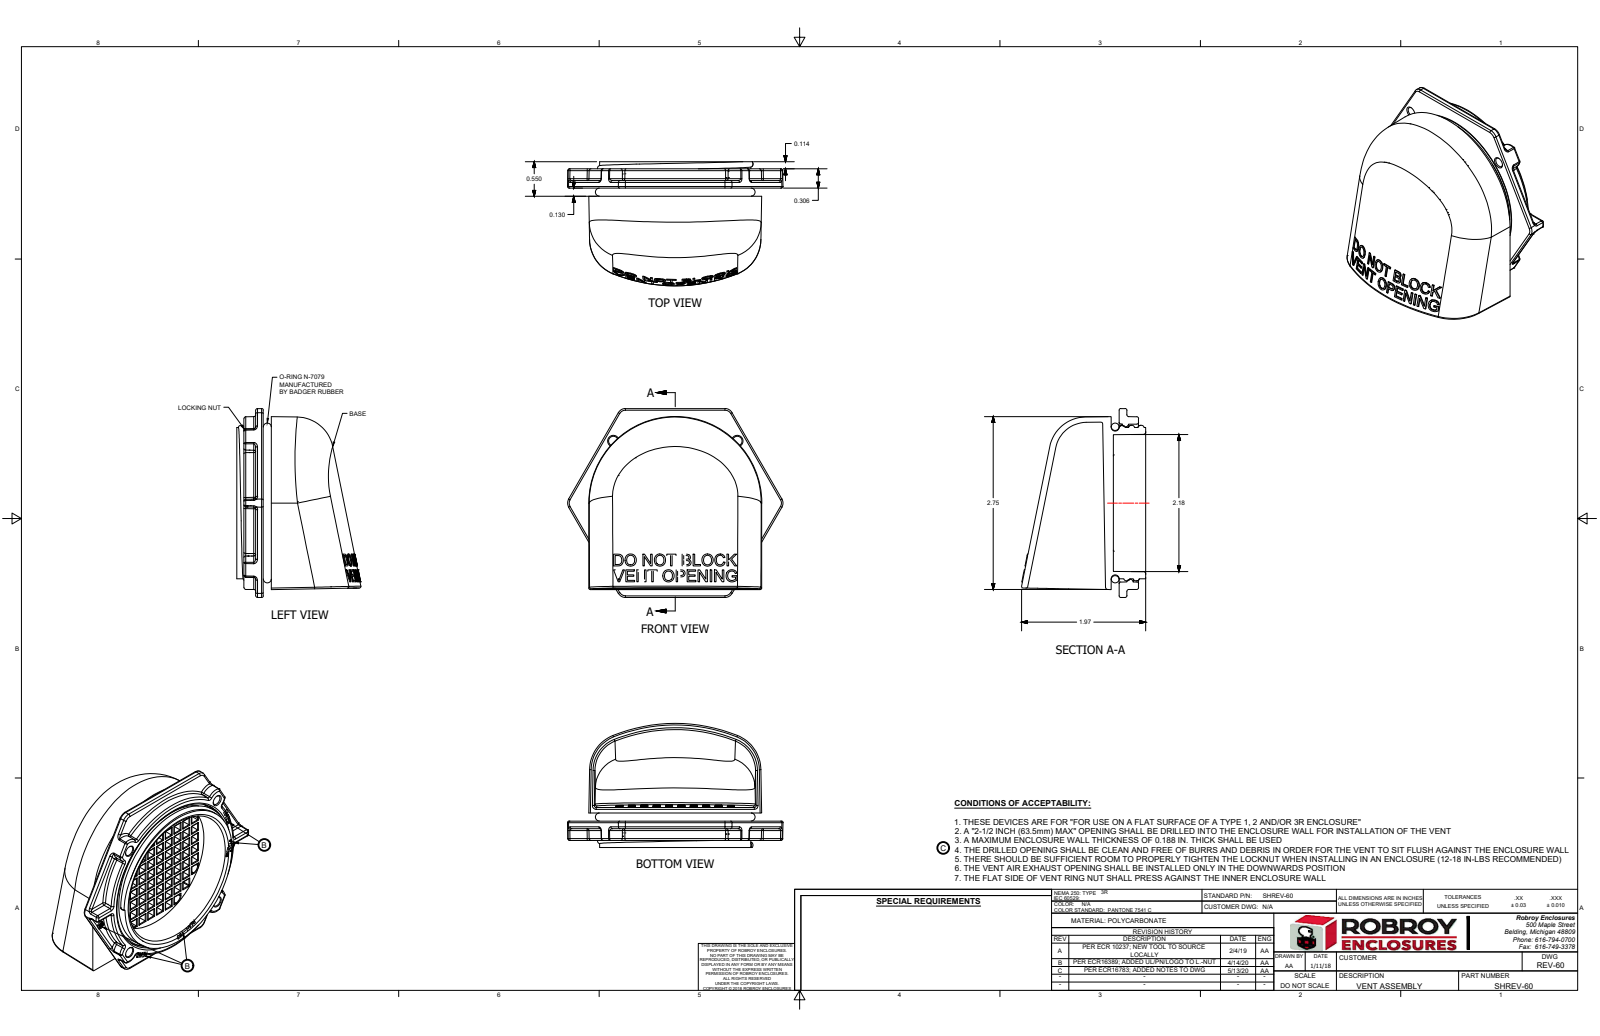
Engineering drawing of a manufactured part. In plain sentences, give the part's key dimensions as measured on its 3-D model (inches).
The part is named "REAHV-60". Its 3-D file was written by "SolidWorks 2019 (AUTOMOTIVE_DESIGN)". It is 3 solids with 1328 faces: 525 planar, 431 cylindrical and 372 other. Overall it measures 3.428 by 3.003 by 1.974 inches. Its volume is 2.839 cubic inches and its surface area 62.42 square inches. Round holes: 1 of diameter 0.15. Round bosses or shafts: 1 of diameter 2.405. Partial cylindrical surfaces (rounded edges, fillets, slot ends): 40 of radius 0.009, 39 of radius 0.03, 12 of radius 0.009, 8 of radius 0.095, 6 of radius 0.025, 5 of radius 0.03, 2 of radius 0.025, 2 of radius 0.079. The main face-to-face distances are 0.196, 0.392, 0.588, 0.784, 0.98, 0.13, 1.176, 0.093, 0.037, 1.372.
